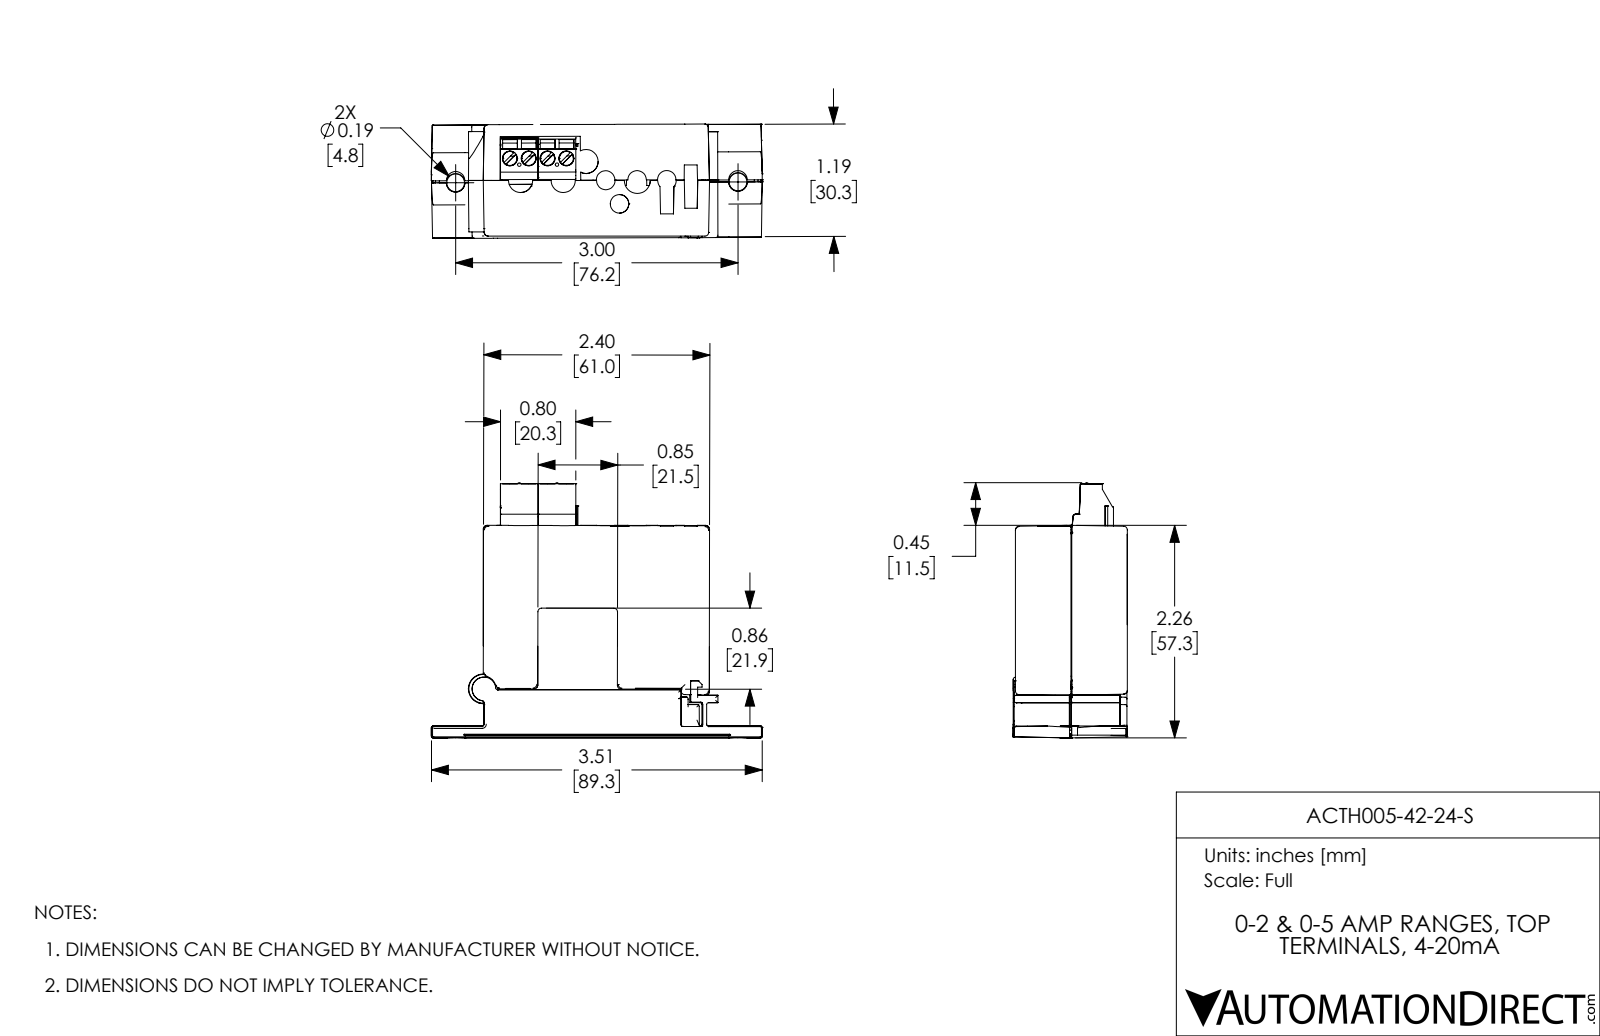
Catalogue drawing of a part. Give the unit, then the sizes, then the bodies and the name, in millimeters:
Units: millimetres
Overall size (bounding box): 89.3 × 68.84 × 30.67
Round holes (diameter × count): ⌀4 ×4, ⌀5 ×3, ⌀1.4 ×2, ⌀0.46 ×1
Round bosses / shafts (diameter × count): ⌀3.8 ×4, ⌀1.3 ×4, ⌀7.77 ×1, ⌀0.46 ×1
Partial cylindrical surfaces — rounded edges, fillets, slot ends (radius × count): R0.5 ×52, R1 ×39, R0.16 ×22, R0.21 ×12, R0.64 ×11, R2.5 ×7, R0.1 ×4, R0.47 ×4
Main face-to-face distances: 2, 1.97, 21.8, 46.3, 36.2, 1.9, 57.78, 9.8, 15, 44.34
Hole centre spacings: 5.08, 9.95, 10.17, 1.64, 1.65, 4.99, 5, 5.09
Volume: 97 479 mm³ · Surface area: 53 626 mm²
Bodies: 6 solids, 1248 faces (801 planar, 266 cylindrical, 181 other)
Part name (STEP PRODUCT): ACTH005-42-24-S
STEP written by: SolidWorks 2017 (AUTOMOTIVE_DESIGN)
